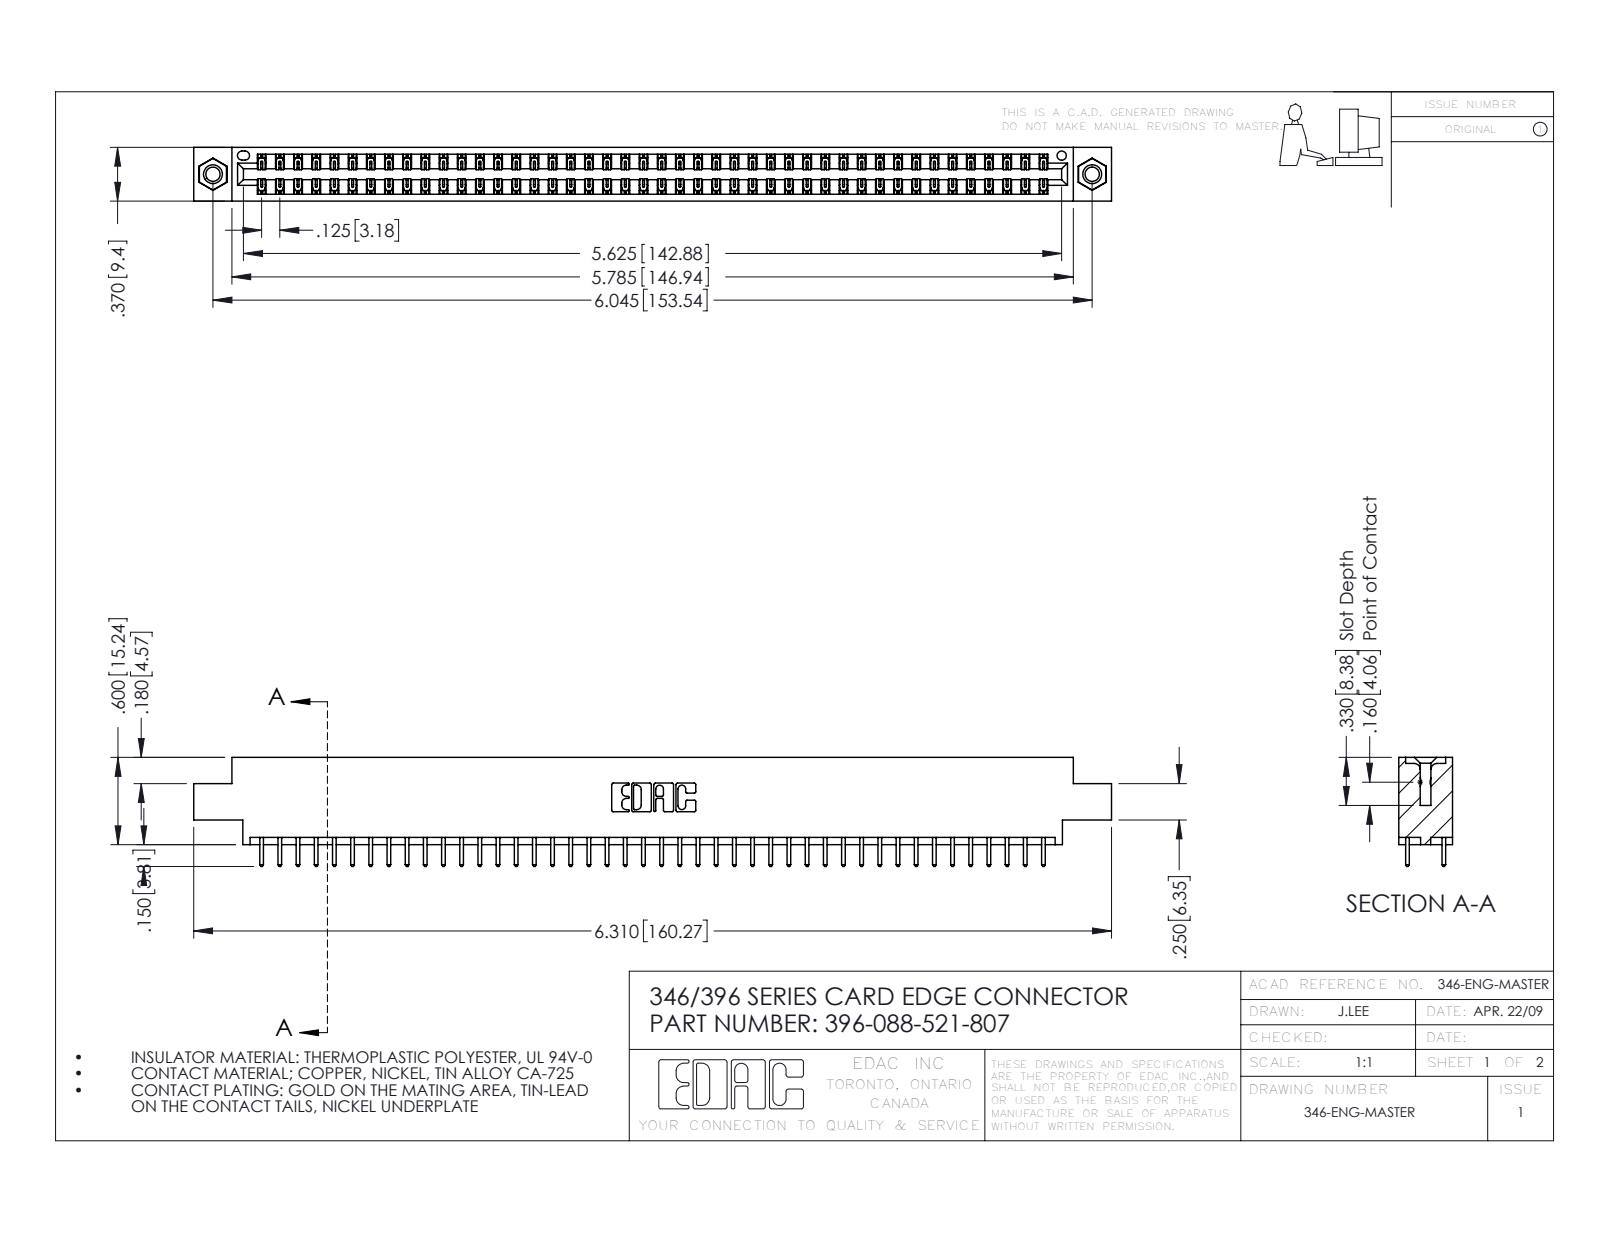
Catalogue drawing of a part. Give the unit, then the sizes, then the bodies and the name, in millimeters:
Units: millimetres
Overall size (bounding box): 160.3 × 19.1 × 9.4
Round holes (diameter × count): ⌀2.5 ×2, ⌀3.2 ×2, ⌀4 ×2, ⌀1.6 ×1
Round bosses / shafts (diameter × count): ⌀3.9 ×2
Partial cylindrical surfaces — rounded edges, fillets, slot ends (radius × count): R0.2 ×132, R0.3 ×88, R0.3 ×22, R0.2 ×6, R0.8 ×6, R0.7 ×3, R0.4 ×2, R0.6 ×2
Main face-to-face distances: 1.2, 8.2, 9.4, 6.4, 1.8, 7.6, 0.6, 7, 5.6, 3.8
Hole centre spacings: 6.2, 148.2, 153.5
Volume: 15 400 mm³ · Surface area: 21 230 mm²
Bodies: 91 solids, 4762 faces (3192 planar, 1554 cylindrical, 16 other)
Part name (STEP PRODUCT): 345-250-001_345-250-005-103; 346 Part_0.170 Offset - 0.156 Dia-TI; 345-292-001_345-293-121; 396-088-521-807
STEP written by: SolidWorks 2016 (CONFIG_CONTROL_DESIGN)
